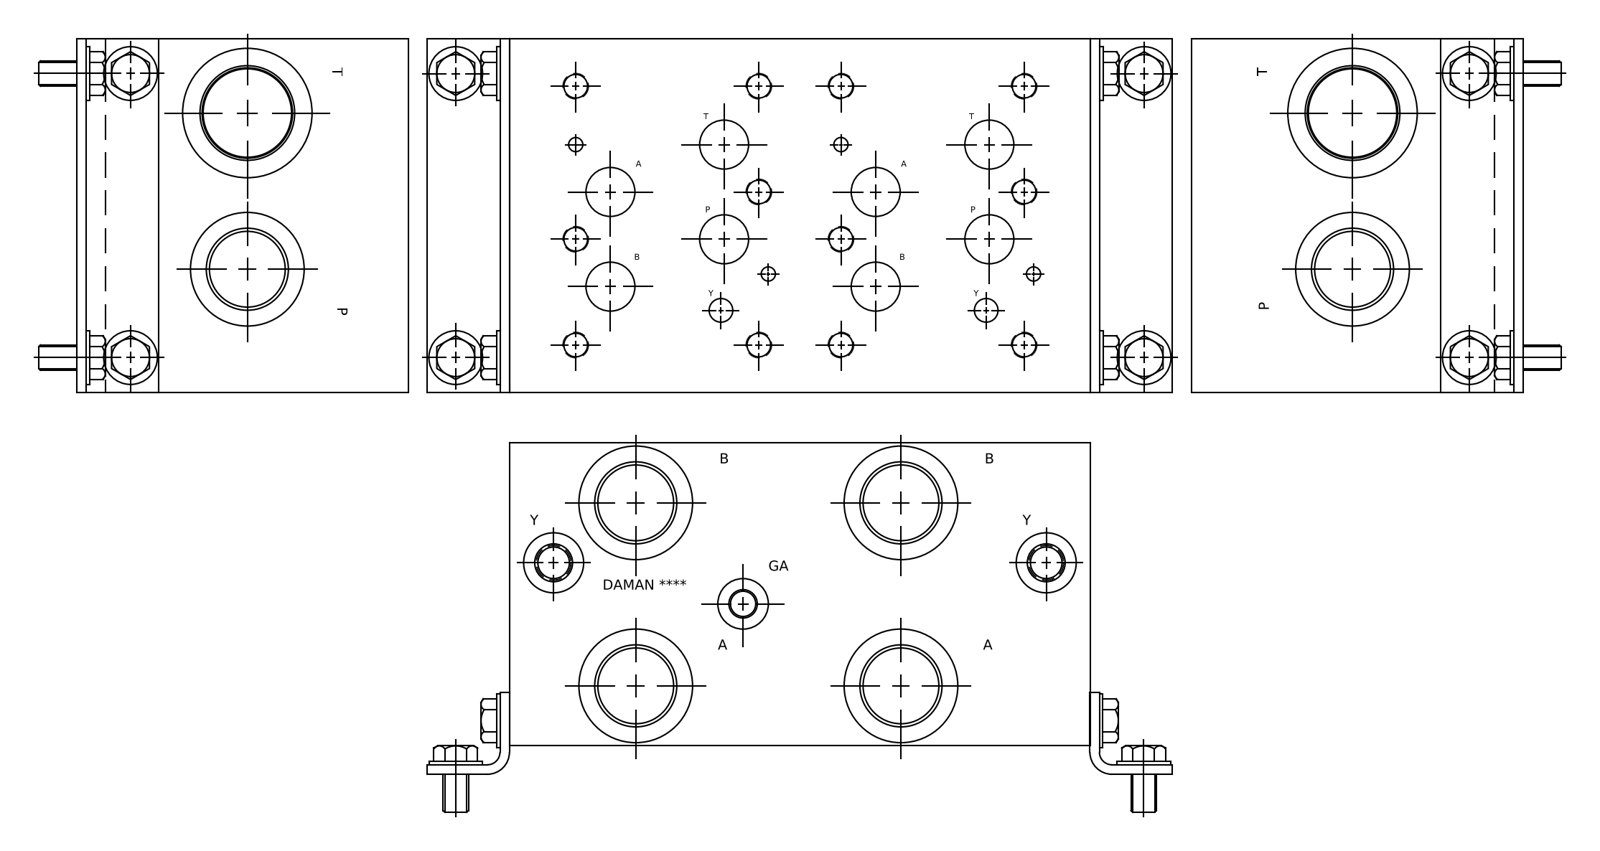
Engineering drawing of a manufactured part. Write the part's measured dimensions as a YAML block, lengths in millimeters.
part_name: "Part_AD08HP025S_3D"
step_written_by: "Autodesk Inventor 2019 (AUTOMOTIVE_DESIGN)"
units: millimeters
bodies: {solids: 1, faces: 729, planar: 389, cylindrical: 101, other: 239}
overall_size: [292.1, 177.8, 152.4]
volume: 7351000
surface_area: 319808
round_holes:
  - {diameter: 10.72, count: 15}
  - {diameter: 12.7, count: 14}
  - {diameter: 24.61, count: 8}
  - {diameter: 39.22, count: 5}
  - {diameter: 58.57, count: 5}
  - {diameter: 7.14, count: 4}
  - {diameter: 36.91, count: 4}
  - {diameter: 41.27, count: 4}
  - {diameter: 43.51, count: 4}
  - {diameter: 14.27, count: 3}
  - {diameter: 11.13, count: 2}
  - {diameter: 17.5, count: 2}
face_to_face_distances: [152.4, 177.8, 292.1, 0.79, 177.01, 291.31, 290.52, 19.84, 19.05, 272.26]
hole_center_spacings: [133.35, 29.53, 47.62, 29.54, 61.92, 74.63, 136.54, 34.17]
